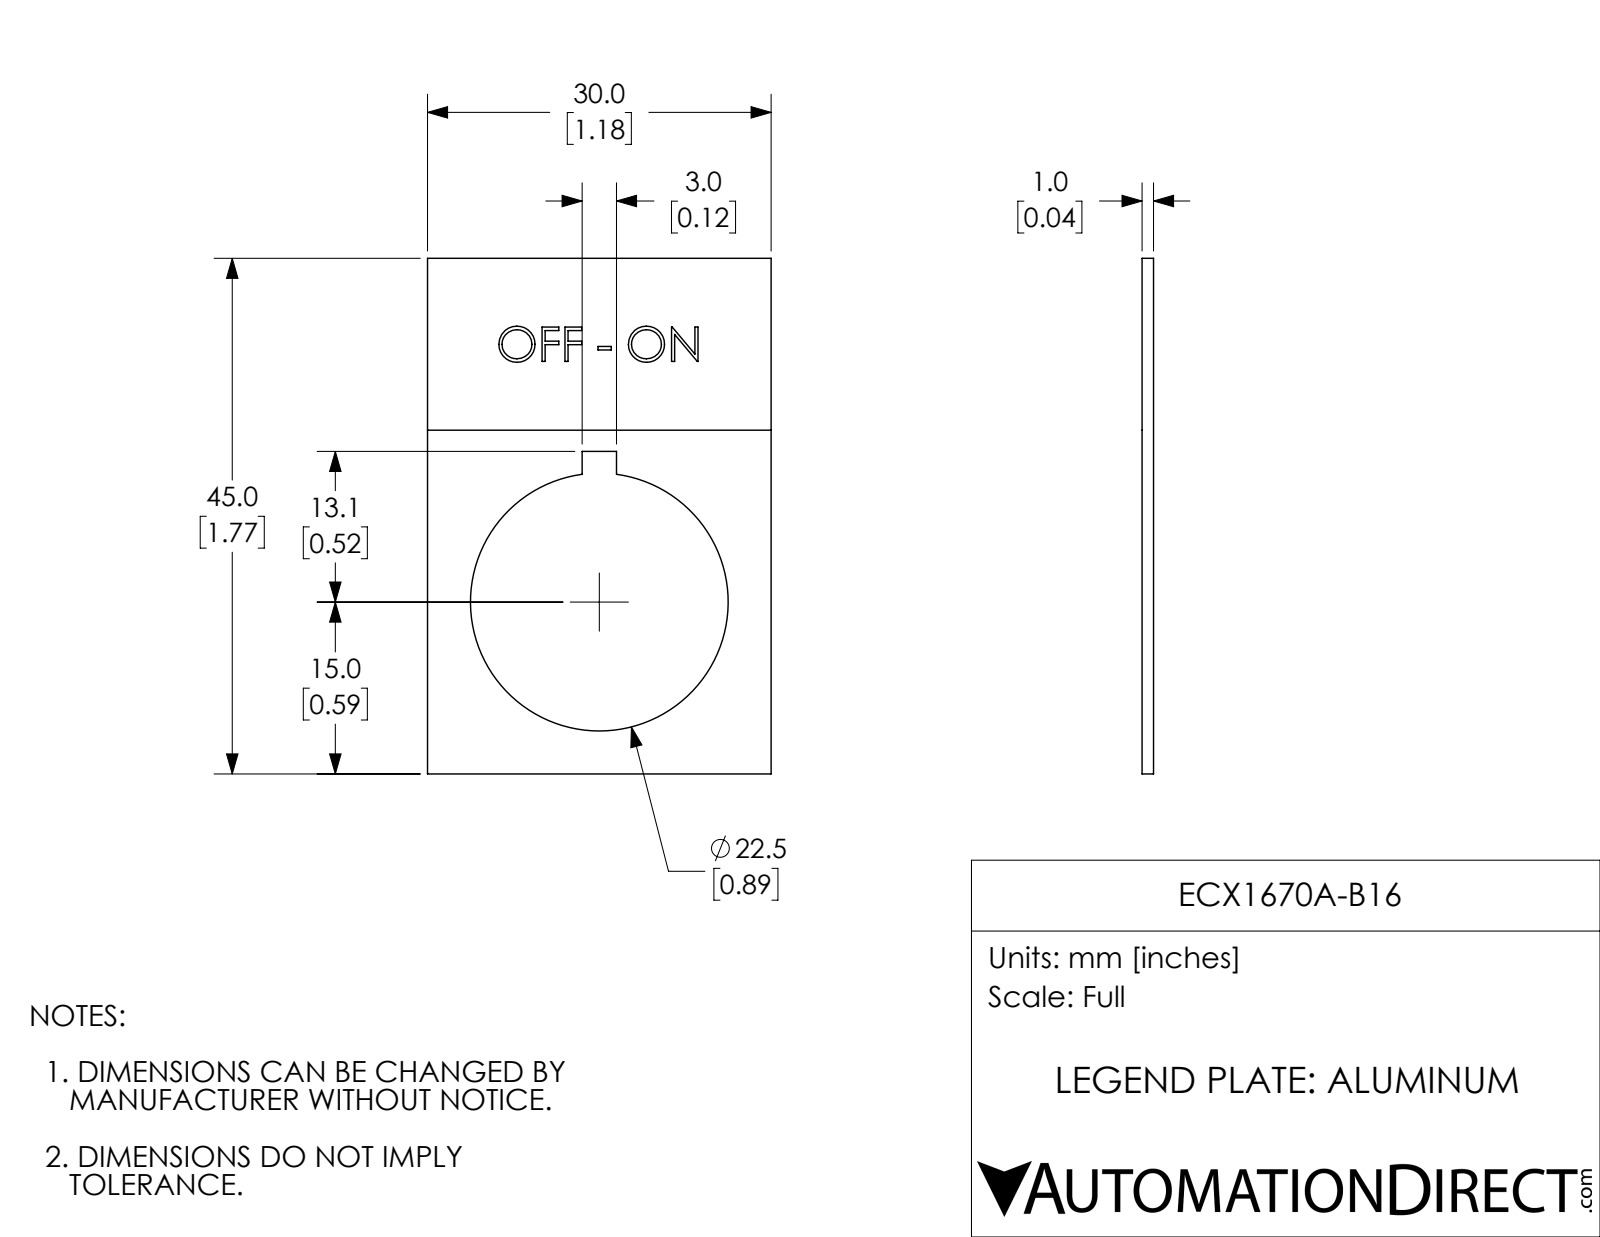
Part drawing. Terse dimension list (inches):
name: ECX1670A-B16
written by: SolidWorks 2017 (AUTOMOTIVE_DESIGN)
unit: in
bodies: 1 solid, 71 faces (52 planar, 3 cylindrical, 16 other)
size: 1.772 × 1.181 × 0.039
volume: 0.058 in³; area: 3.286 in²
holes: 1× ⌀0.886
face distances: 0.039, 1.181, 1.772, 0.038, 0.531, 0.65, 1.108, 0.663, 0.118, 0.367
